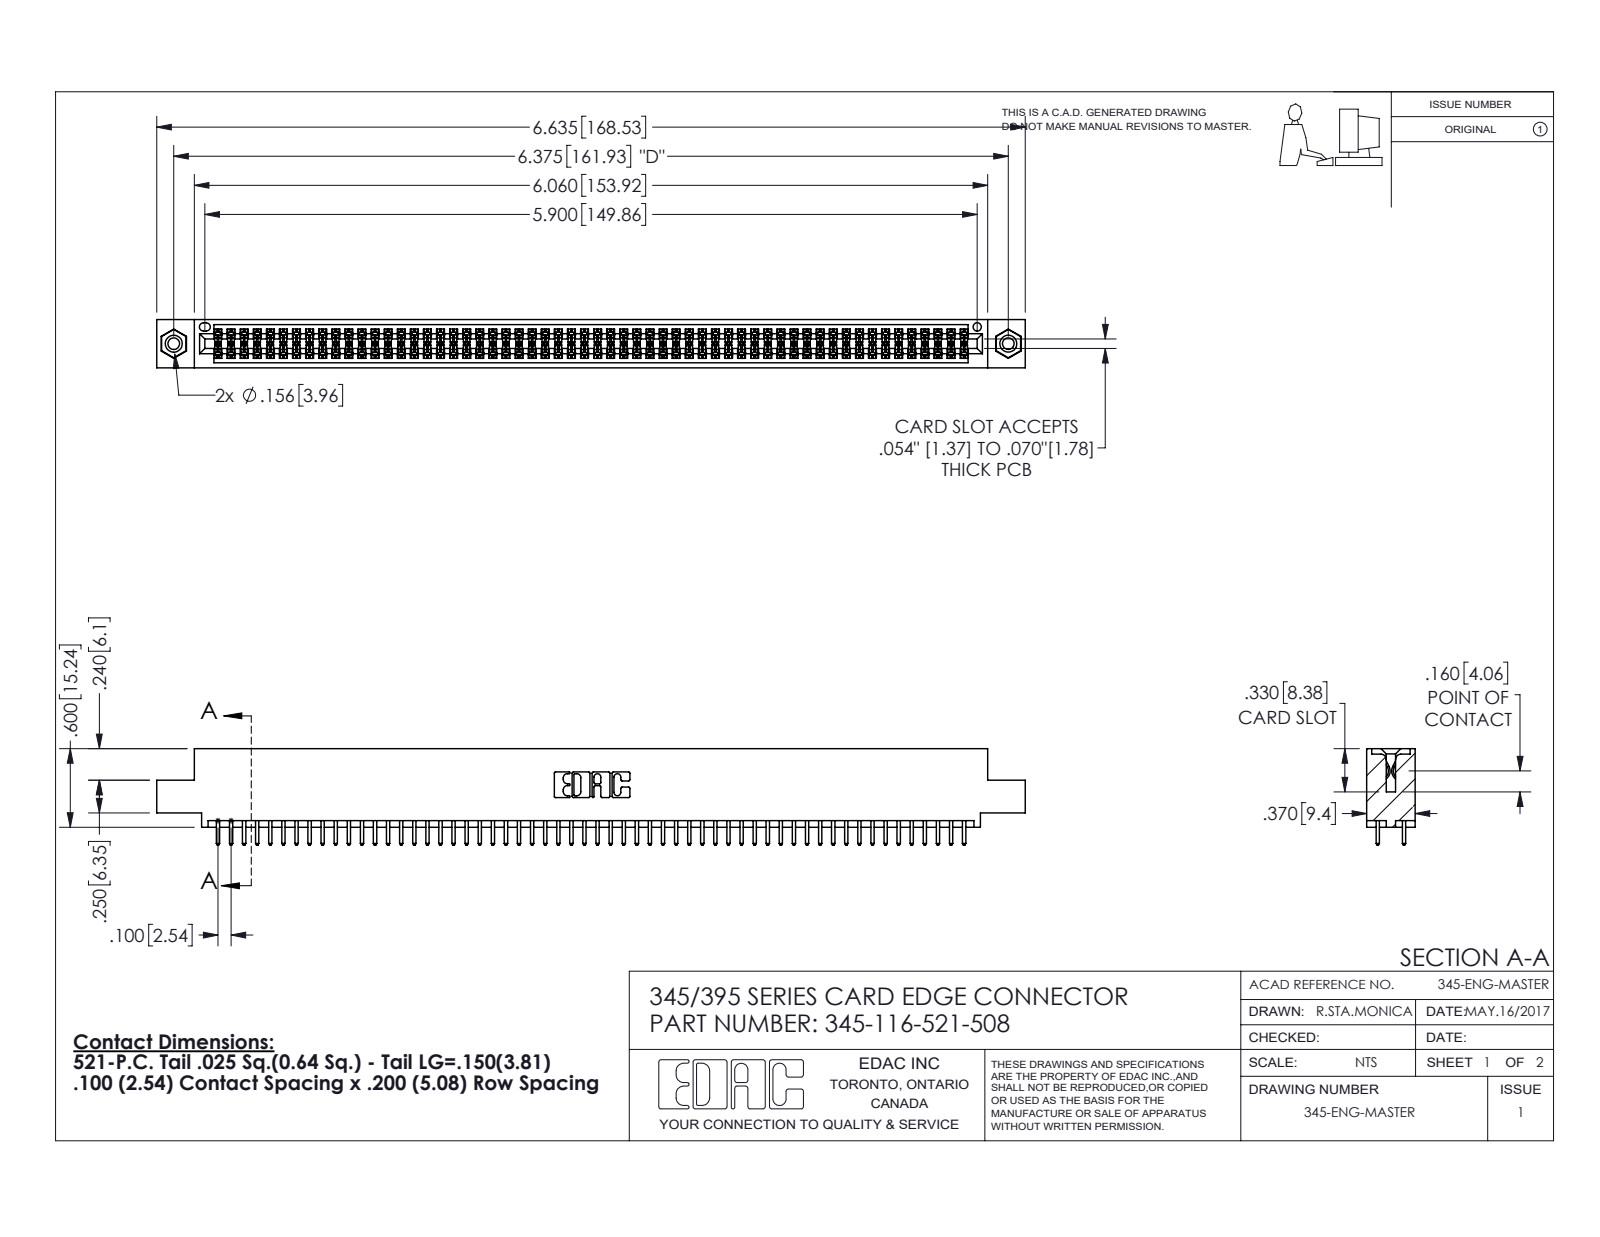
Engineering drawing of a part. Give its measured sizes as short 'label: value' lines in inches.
name: 345 Part_0.110 Offset - 0.156 Dia-TI; 345-250-001_345-250-003-102; 345-116-521-508; 345-292-001_345-293-121
written by: SolidWorks 2016 (CONFIG_CONTROL_DESIGN)
unit: in
bodies: 119 solids, 5990 faces (3944 planar, 2030 cylindrical, 16 other)
size: 6.635 × 0.737 × 0.37
volume: 1 in³; area: 37.72 in²
holes: 2× ⌀0.089, 2× ⌀0.125, 2× ⌀0.156, 1× ⌀0.064
bosses: 2× ⌀0.155
rounds: 174× R0.006, 116× R0.01, 22× R0.01, 6× R0.007, 6× R0.031, 3× R0.026, 2× R0.014, 2× R0.019
face distances: 0.072, 0.298, 0.2, 0.098, 0.272, 0.025, 0.37, 0.225, 0.175, 0.149
hole spacings: 0.27, 6.139, 6.375
